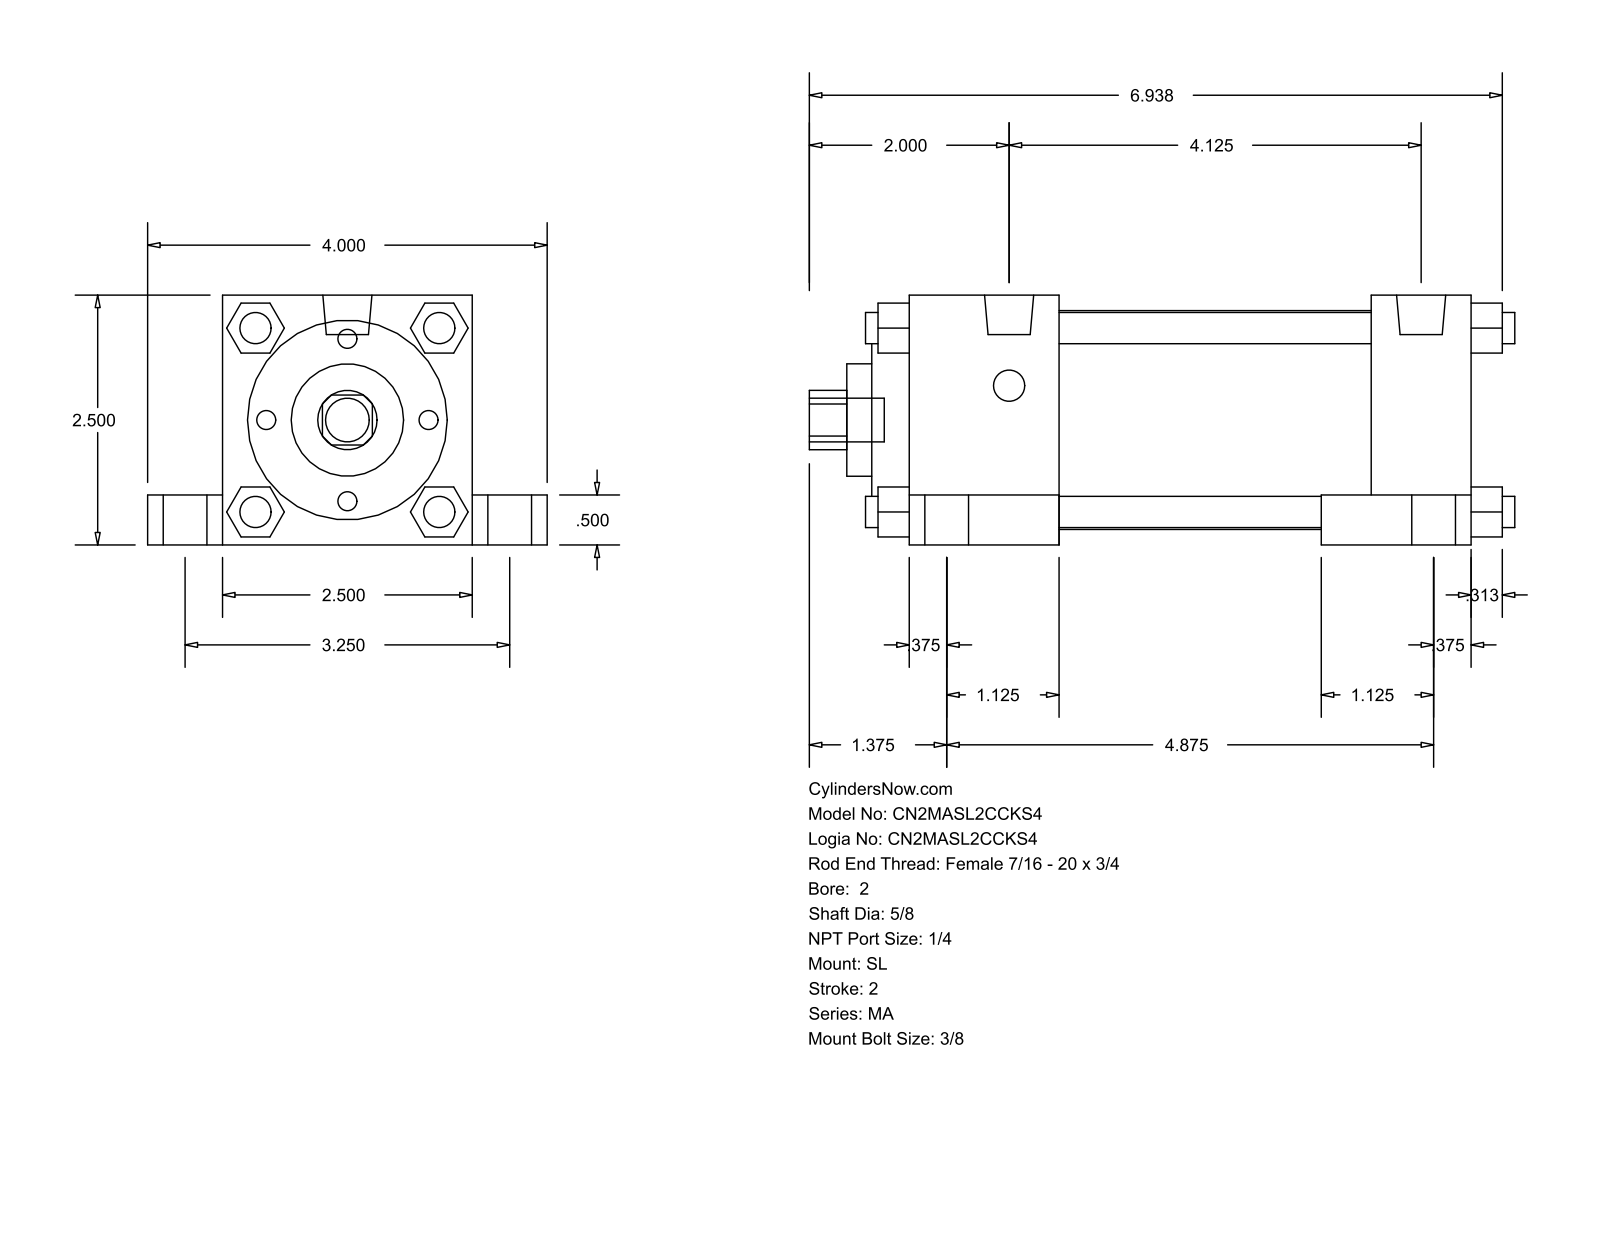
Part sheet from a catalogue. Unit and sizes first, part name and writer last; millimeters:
Units: millimetres
Overall size (bounding box): 179.39 × 101.6 × 63.5
Round holes (diameter × count): ⌀15.88 ×1, ⌀28.57 ×1, ⌀50.8 ×1, ⌀55.63 ×1
Round bosses / shafts (diameter × count): ⌀7.94 ×8, ⌀11.11 ×5, ⌀17.46 ×4, ⌀12.49 ×2
Partial cylindrical surfaces — rounded edges, fillets, slot ends (radius × count): R7.54 ×1
Main face-to-face distances: 63.5, 12.7, 9.52, 25.4, 19.05, 82.55, 38.1, 142.88, 50.8, 104.78
Bodies: 0 solids, 150 faces (113 planar, 37 cylindrical, 0 other)
Part name (STEP PRODUCT): MA_SL__0200_0.625
STEP written by: GSSL Pune (CONFIG_CONTROL_DESIGN)
